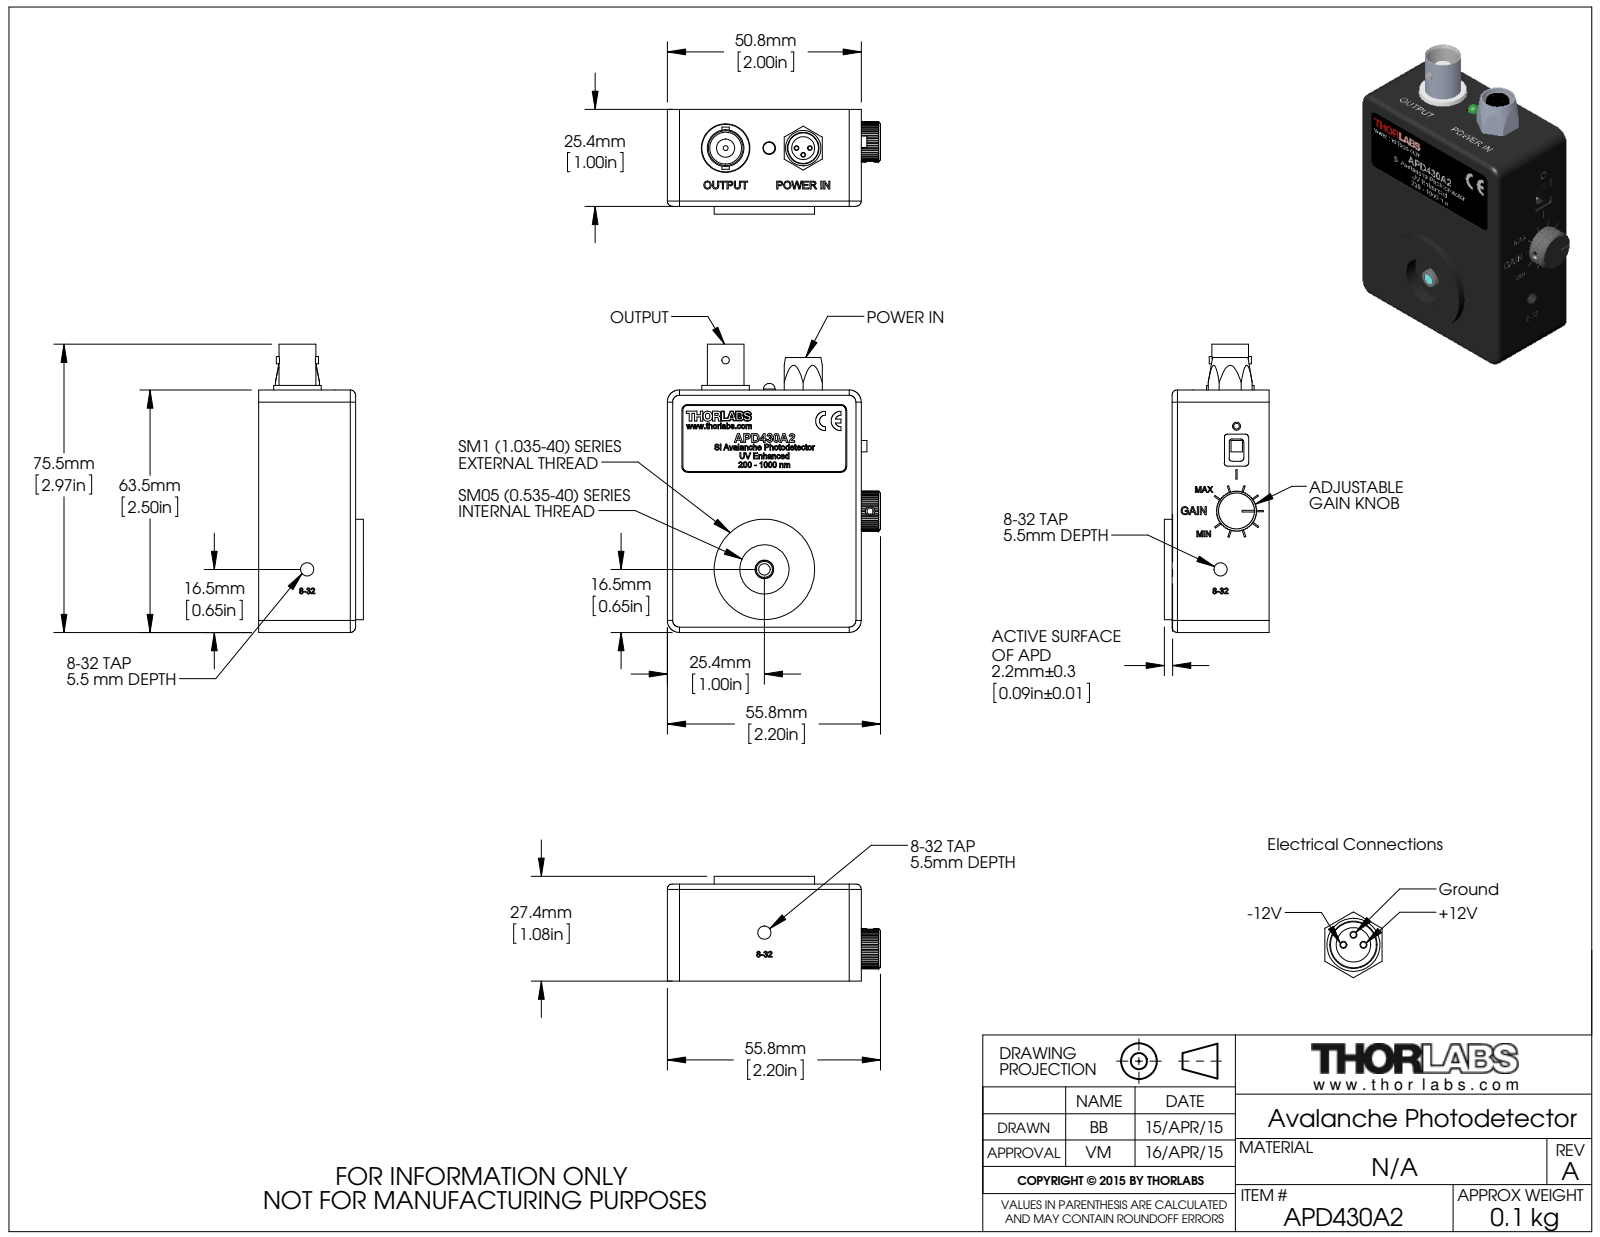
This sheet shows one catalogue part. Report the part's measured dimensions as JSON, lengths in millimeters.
{"part_name": "MTN004939", "step_written_by": "SolidWorks 2014 (AUTOMOTIVE_DESIGN)", "units": "millimeters", "bodies": {"solids": 0, "faces": 2555, "planar": 1306, "cylindrical": 436, "other": 813}, "overall_size": [75.46, 55.8, 27.43], "round_holes": [[1.6, 9], [0.51, 6], [2.4, 4], [0.45, 2], [2.5, 2], [3.45, 2], [1.27, 1], [1.32, 1], [2.1, 1], [3, 1], [3.3, 1], [3.5, 1]], "round_bosses_or_shafts": [[1, 5], [3.8, 4], [2, 4], [1.64, 2], [1.6, 2], [1.3, 2], [26.29, 1], [12.45, 1]], "partial_cylinders_radius": [[0.3, 53], [3.17, 19], [3.3, 14], [0.79, 8], [2.41, 8], [0.5, 6], [1.91, 6], [0.2, 5]], "face_to_face_distances": [1.59, 2.54, 0.4, 23.75, 22.16, 1.65, 25.4, 23.81, 25, 23.41], "hole_center_spacings": [41.17, 4.41, 51.14, 65.51, 2.49, 43.46, 1.27, 2]}
